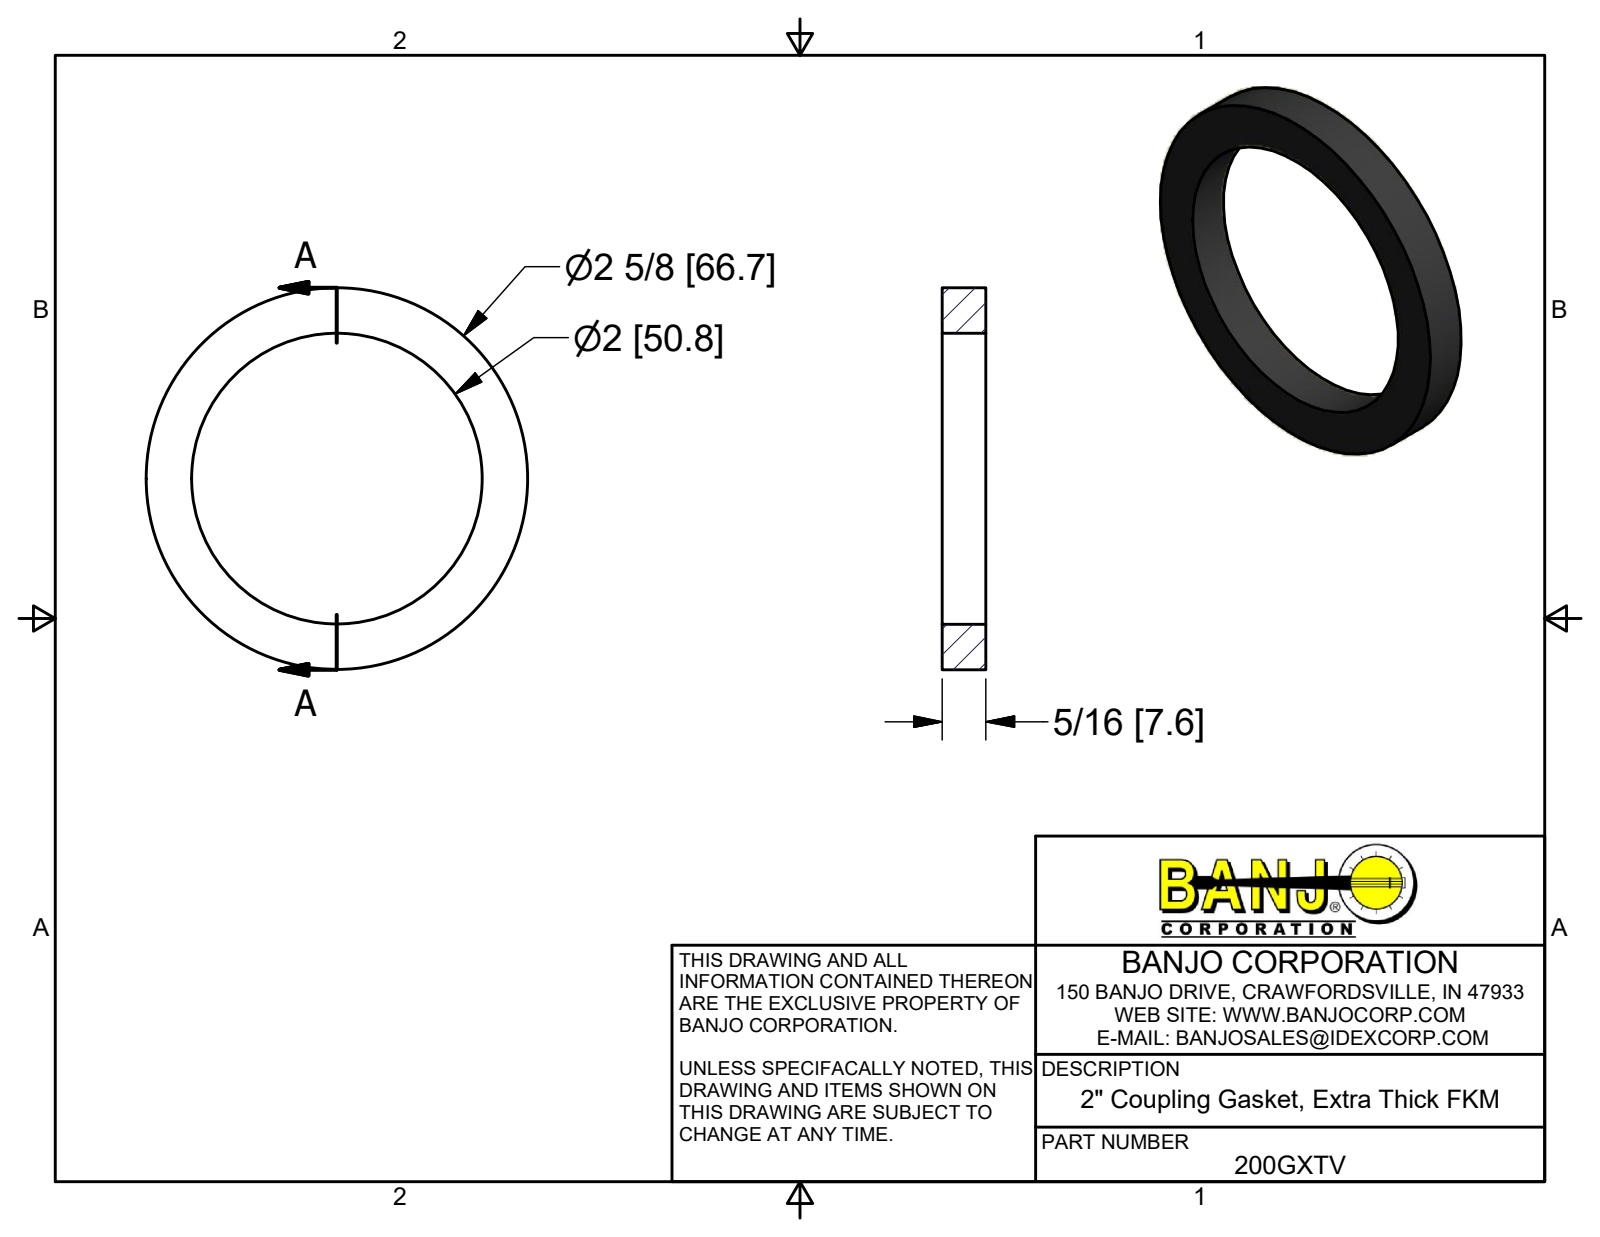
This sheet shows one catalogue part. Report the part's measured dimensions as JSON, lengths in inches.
{"part_name": "200GXTV", "step_written_by": "Autodesk Inventor 2017 (AUTOMOTIVE_DESIGN)", "units": "inches", "bodies": {"solids": 1, "faces": 4, "planar": 2, "cylindrical": 2, "other": 0}, "overall_size": [2.625, 2.625, 0.3], "volume_in3": 0.681, "surface_area_in2": 8.9, "round_holes": [[2, 1]], "round_bosses_or_shafts": [[2.625, 1]], "face_to_face_distances": [0.3]}
